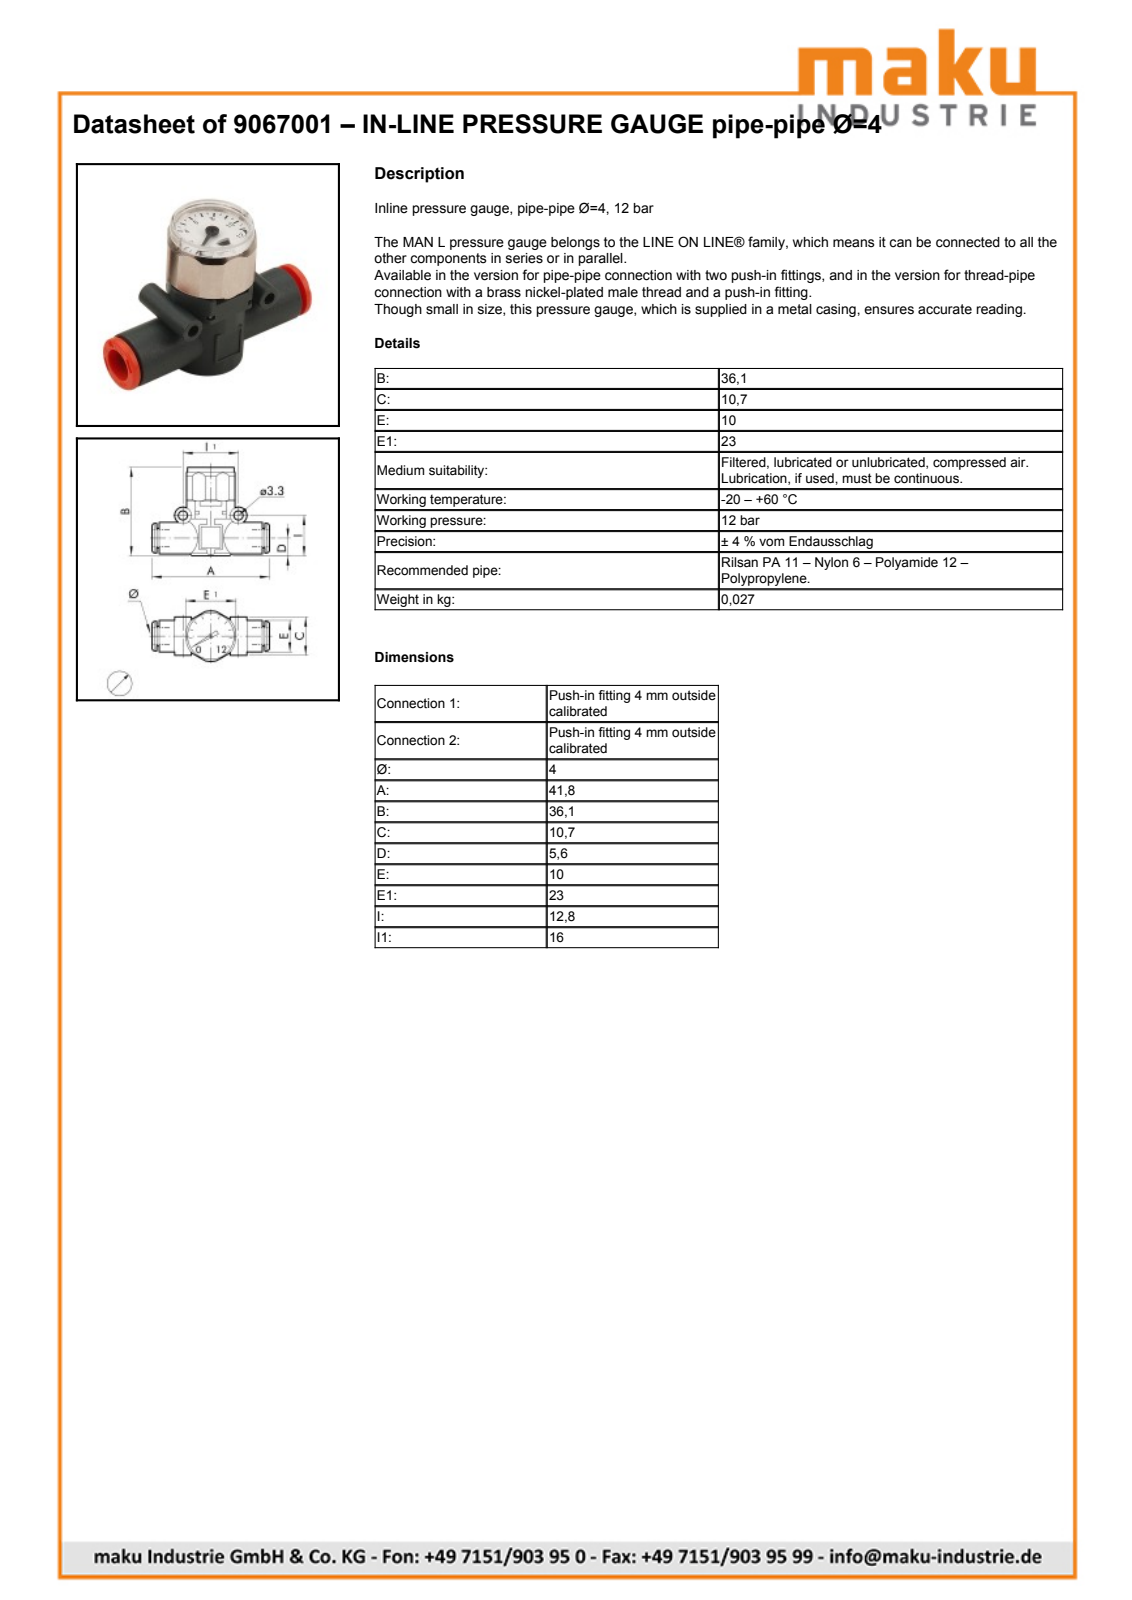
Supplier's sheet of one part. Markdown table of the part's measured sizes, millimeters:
| quantity | value |
| --- | --- |
| part name | 9067001; LINE-ON-LINE D4 V2v/V3V_L body; LINE-ON-LINE D4 VNR-L bushing; LINE ON LINE D4 MAN-L man |
| STEP written by | PARTsolutions (AUTOMOTIVE_DESIGN) |
| units | millimeters |
| bodies | 4 solids, 214 faces (149 planar, 57 cylindrical, 8 other) |
| overall size | 41.8 × 36.1 × 22.73 |
| volume | 8 792 mm³ |
| surface area | 6 035 mm² |
| round holes (diameter × count) | 3.3 × 2, 3.6 × 1, 4 × 1, 4.1 × 1, 6 × 1, 6.5 × 1, 7.5 × 1, 7.8 × 1, 8.1 × 1, 17.61 × 1, 18.86 × 1 |
| round bosses / shafts (diameter × count) | 6 × 2, 20.96 × 1, 17.91 × 1, 11 × 1, 9.2 × 1, 9 × 1, 6.2 × 1 |
| partial cylindrical surfaces (radius × count) | 0.71 × 1, 3.75 × 1, 5.65 × 1, 5.7 × 1, 6.9 × 1, 11.5 × 1 |
| main face-to-face distances | 14.41, 22, 16.25, 6, 16, 5.75, 5.21, 19.62, 10.2, 4.75 |
| hole center spacings | 10.76, 16 |
